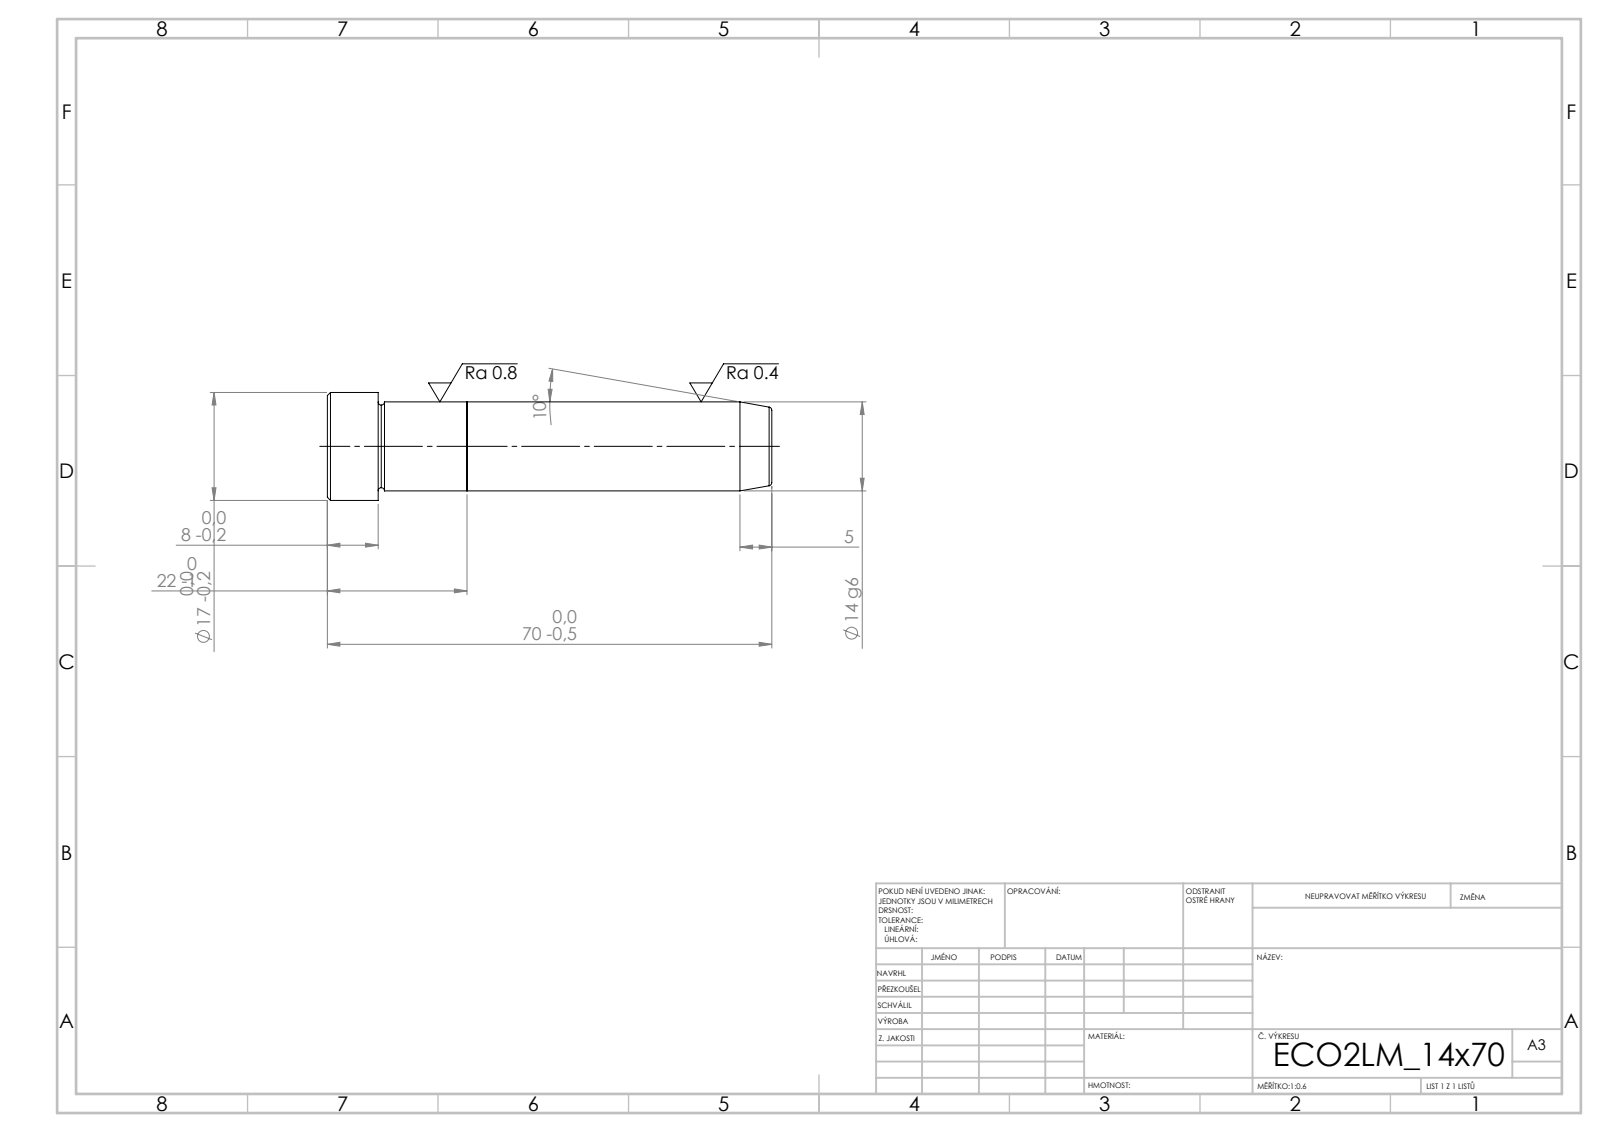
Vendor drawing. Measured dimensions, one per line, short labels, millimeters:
written by: SolidWorks 2019 (CONFIG_CONTROL_DESIGN)
unit: mm
bodies: 2 solids, 21 faces (5 planar, 6 cylindrical, 10 other)
size: 70 × 17 × 17
volume: 11 242 mm³; area: 3 869 mm²
bosses: 1× ⌀17, 1× ⌀14
face distances: 22, 48, 70, 62, 14, 8
